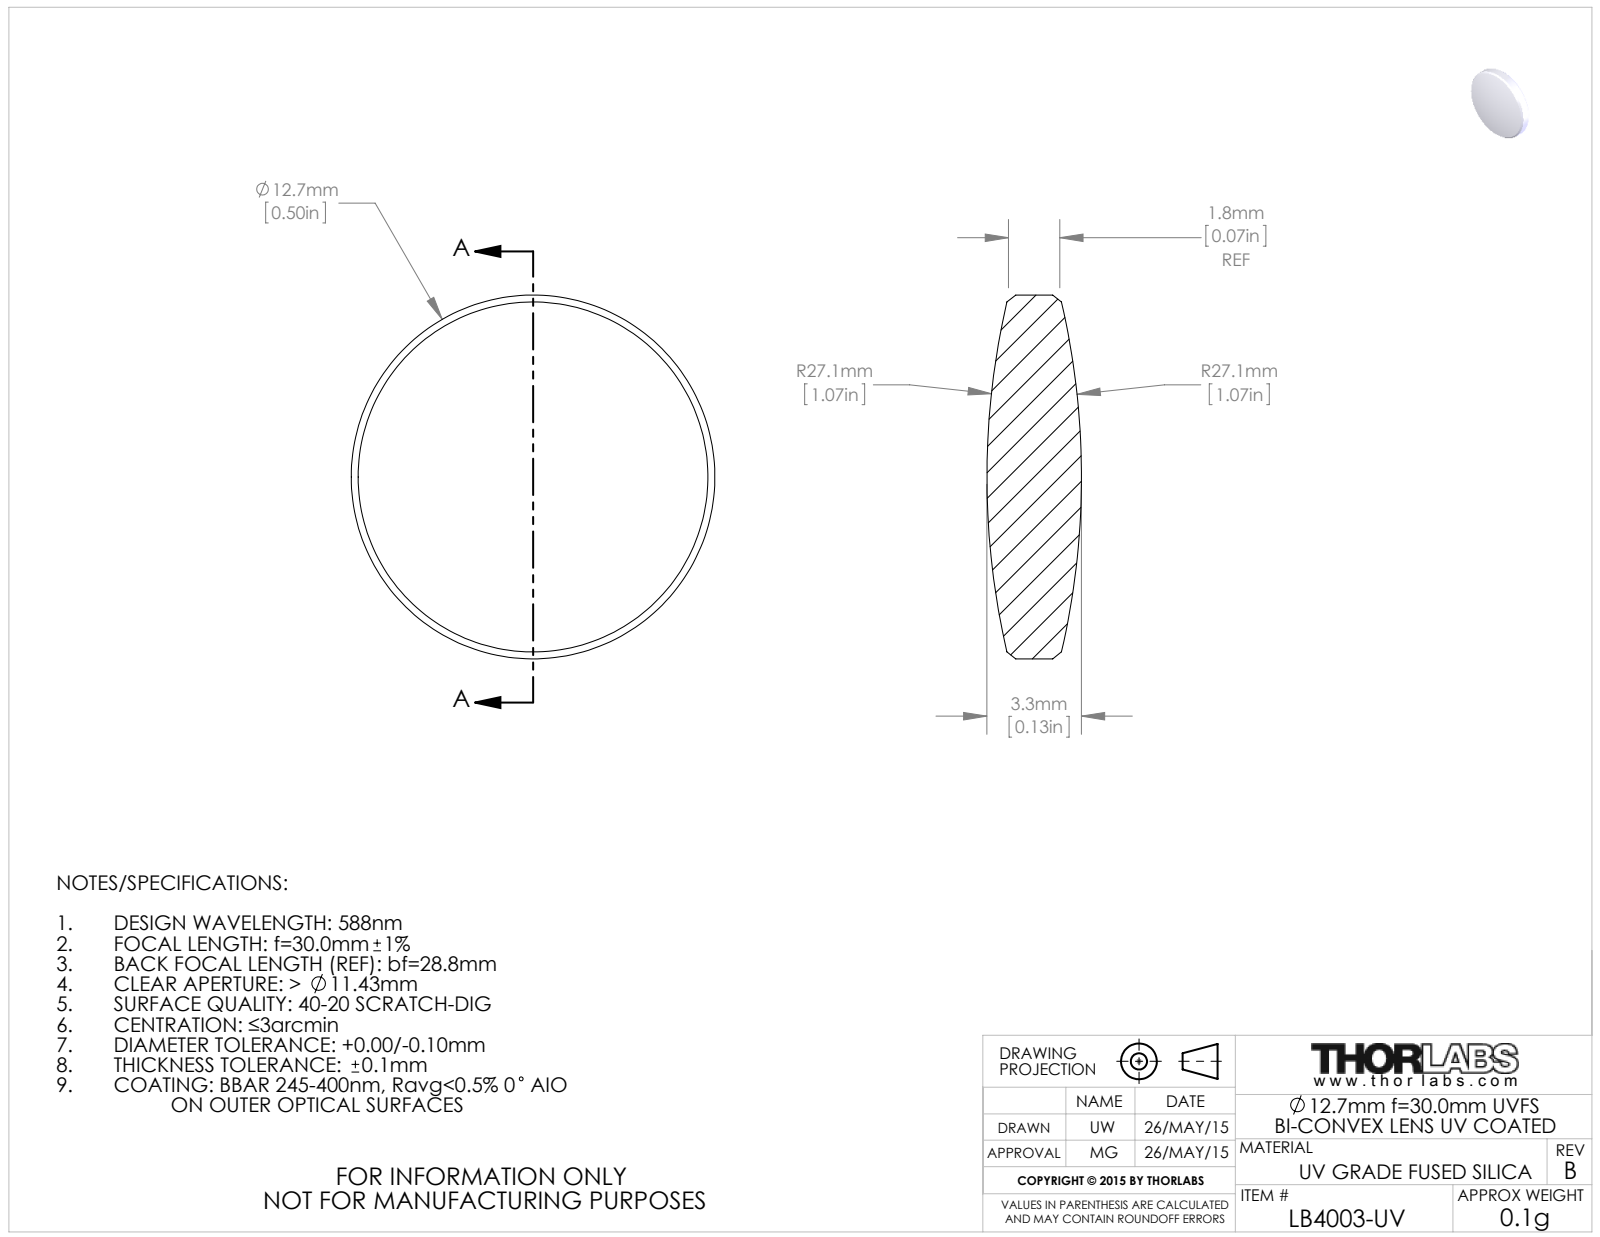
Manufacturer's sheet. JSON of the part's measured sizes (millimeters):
{"part_name": "4312-E0W", "step_written_by": "SolidWorks 2014 (CONFIG_CONTROL_DESIGN)", "units": "millimeters", "bodies": {"solids": 1, "faces": 10, "planar": 0, "cylindrical": 2, "other": 8}, "overall_size": [12.7, 12.7, 3.3], "volume_mm3": 321, "surface_area_mm2": 320, "round_bosses_or_shafts": [[12.7, 1]]}
